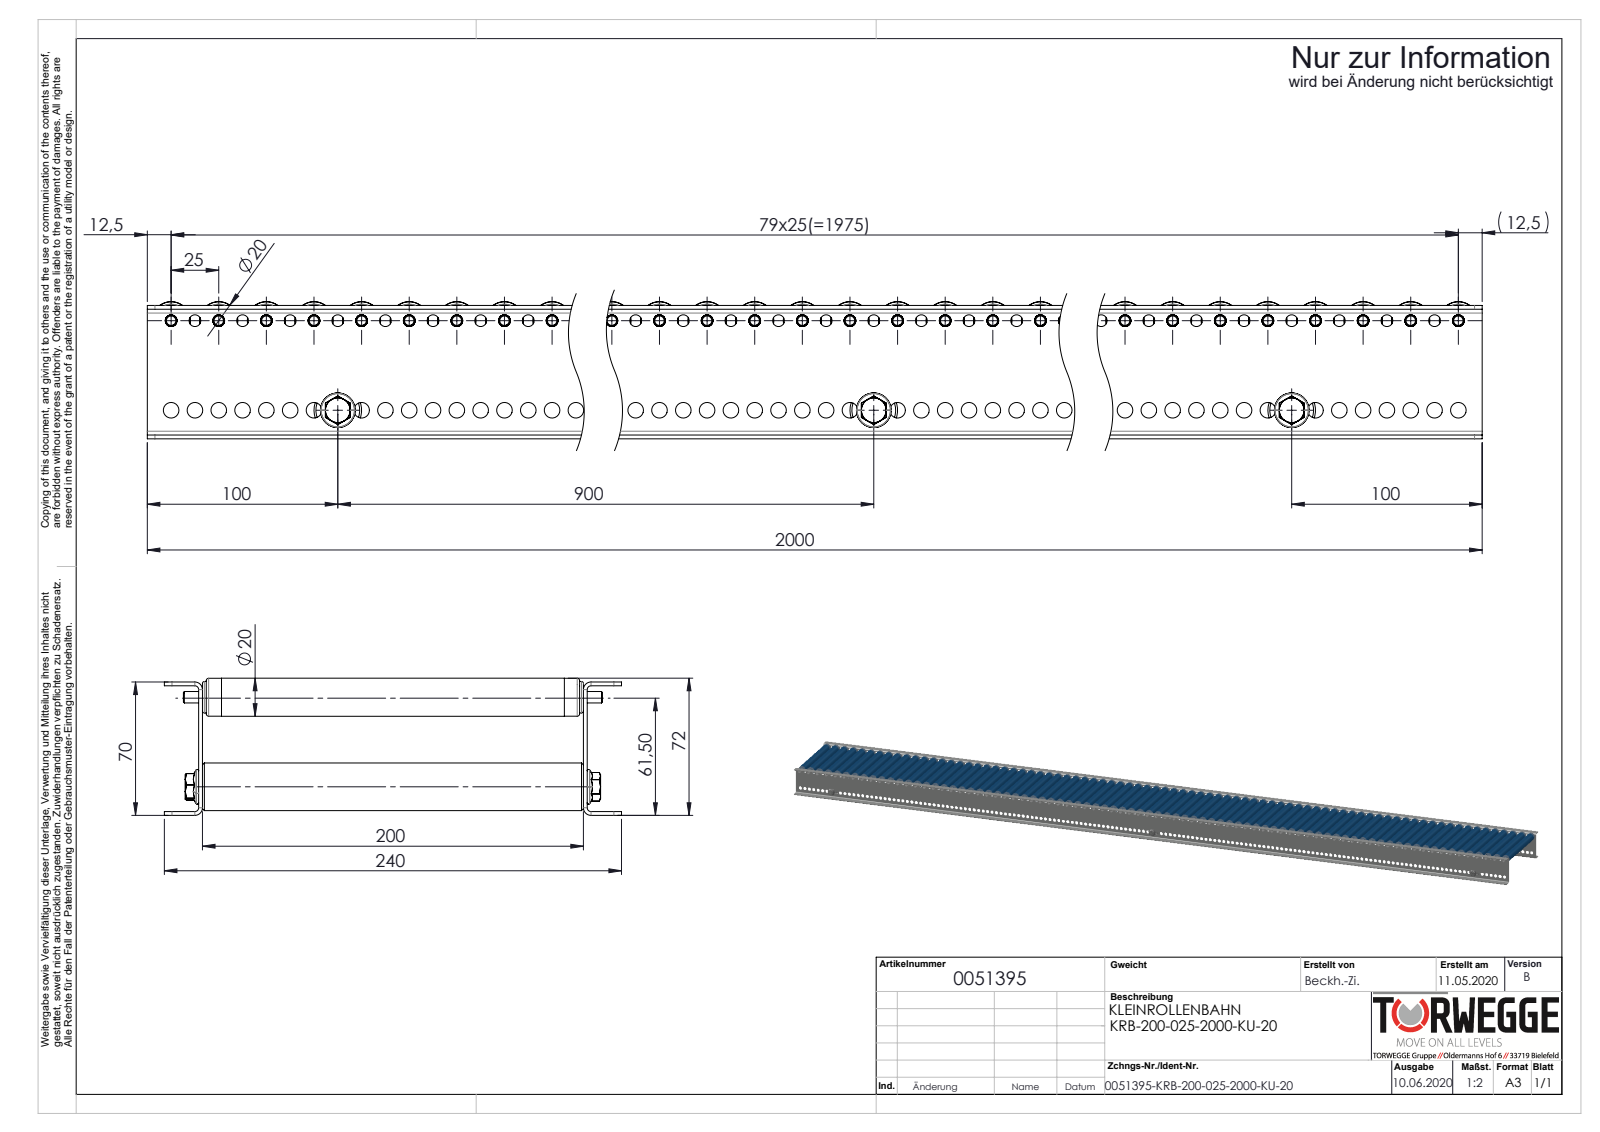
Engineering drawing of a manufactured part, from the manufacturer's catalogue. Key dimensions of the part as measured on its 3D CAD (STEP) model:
Part name (STEP PRODUCT): Profil_KRB-20x70x20x2_KFG_S100206_U-PROFIL-20-70-20-2-KRB-20-L=2000; 0026257_TYP-KUT50-20X1,5-6; 0039777_Achse-Ø06-FA-KFG_L=220 fr D20; 0051395 (+4 more)
STEP written by: SolidWorks 2020 (AUTOMOTIVE_DESIGN)
Units: millimetres
Bodies: 497 solids, 21168 faces (7030 planar, 7890 cylindrical, 6248 other)
Overall size (bounding box): 2000 × 240 × 71
Volume: 3 393 000 mm³ · Surface area: 3 598 000 mm²
Round holes (diameter × count): ⌀6.2 ×159, ⌀8.2 ×159, ⌀6.1 ×80, ⌀12.4 ×80, ⌀13.2 ×80, ⌀14.6 ×80, ⌀16.2 ×80, ⌀17 ×80, ⌀17.2 ×80, ⌀6.8 ×3
Round bosses / shafts (diameter × count): ⌀20 ×80, ⌀19.9 ×80, ⌀17.1 ×80, ⌀16.8 ×80, ⌀16.5 ×80, ⌀11.4 ×80, ⌀11.1 ×80, ⌀10.2 ×80
Partial cylindrical surfaces — rounded edges, fillets, slot ends (radius × count): R4.05 ×80, R4 ×8, R2 ×4
Main face-to-face distances: 2, 202, 68, 200, 204, 70, 66, 192, 10, 12
Hole centre spacings: 12.5, 25, 37.5, 50, 62.5, 75, 87.5, 100
